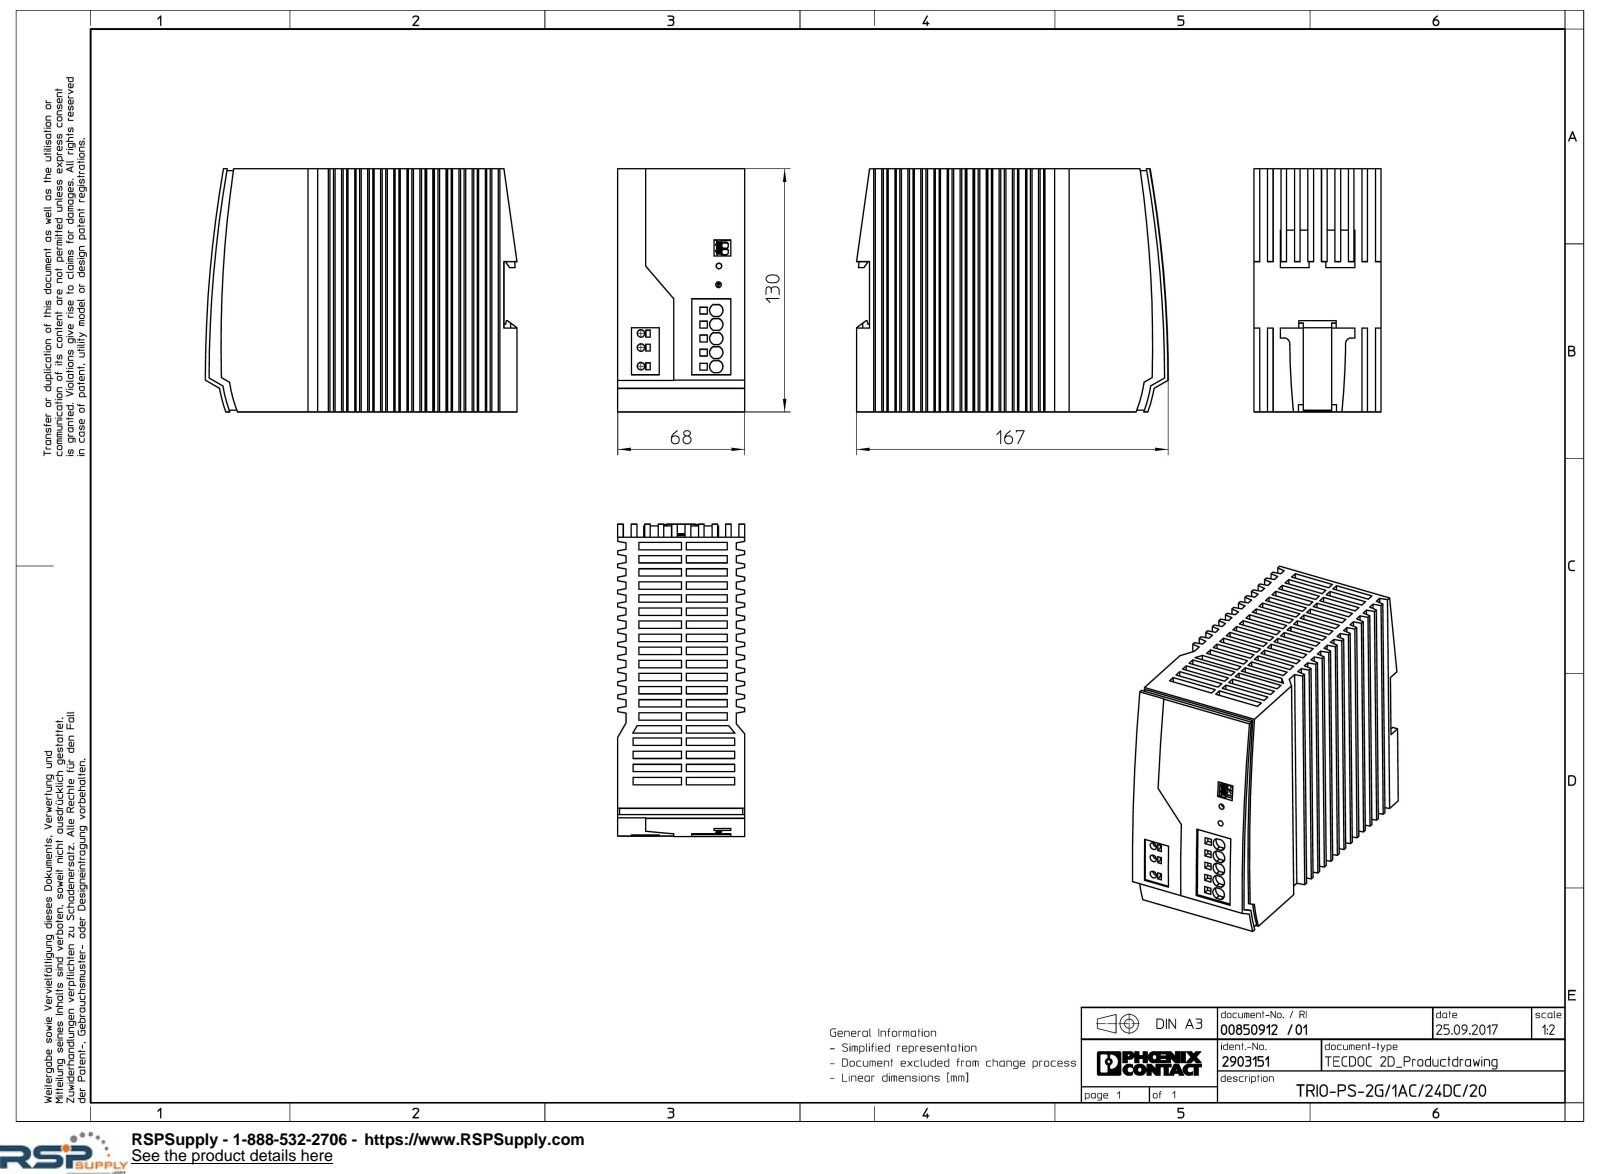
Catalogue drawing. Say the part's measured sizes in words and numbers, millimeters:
The part is named "TRIO_PS_2G_1AC_24DC_20-select". Its 3-D file was written by "Creo Elements/Direct Modeling 18.1I 14-Aug-2016 (C) Parametric Technology GmbH (AUTOMOTIVE_DESIGN)". It is 1 solid with 792 faces: 742 planar, 45 cylindrical and 5 other. Overall it measures 167 by 130 by 68 millimeters. Its volume is 1 298 000 cubic millimeters and its surface area 126 504 square millimeters. Round holes: 3 of diameter 4, 2 of diameter 3. Partial cylindrical surfaces (rounded edges, fillets, slot ends): 10 of radius 3.45, 2 of radius 0.57, 2 of radius 0.6, 2 of radius 1.03, 2 of radius 1.04, 2 of radius 3, 2 of radius 430, 1 of radius 40. The main face-to-face distances are 13.79, 27.58, 4.5, 63.5, 41.37, 6.89, 68, 3, 55.16, 6.9. The hole center spacings are 7.5, 10, 17.5.
